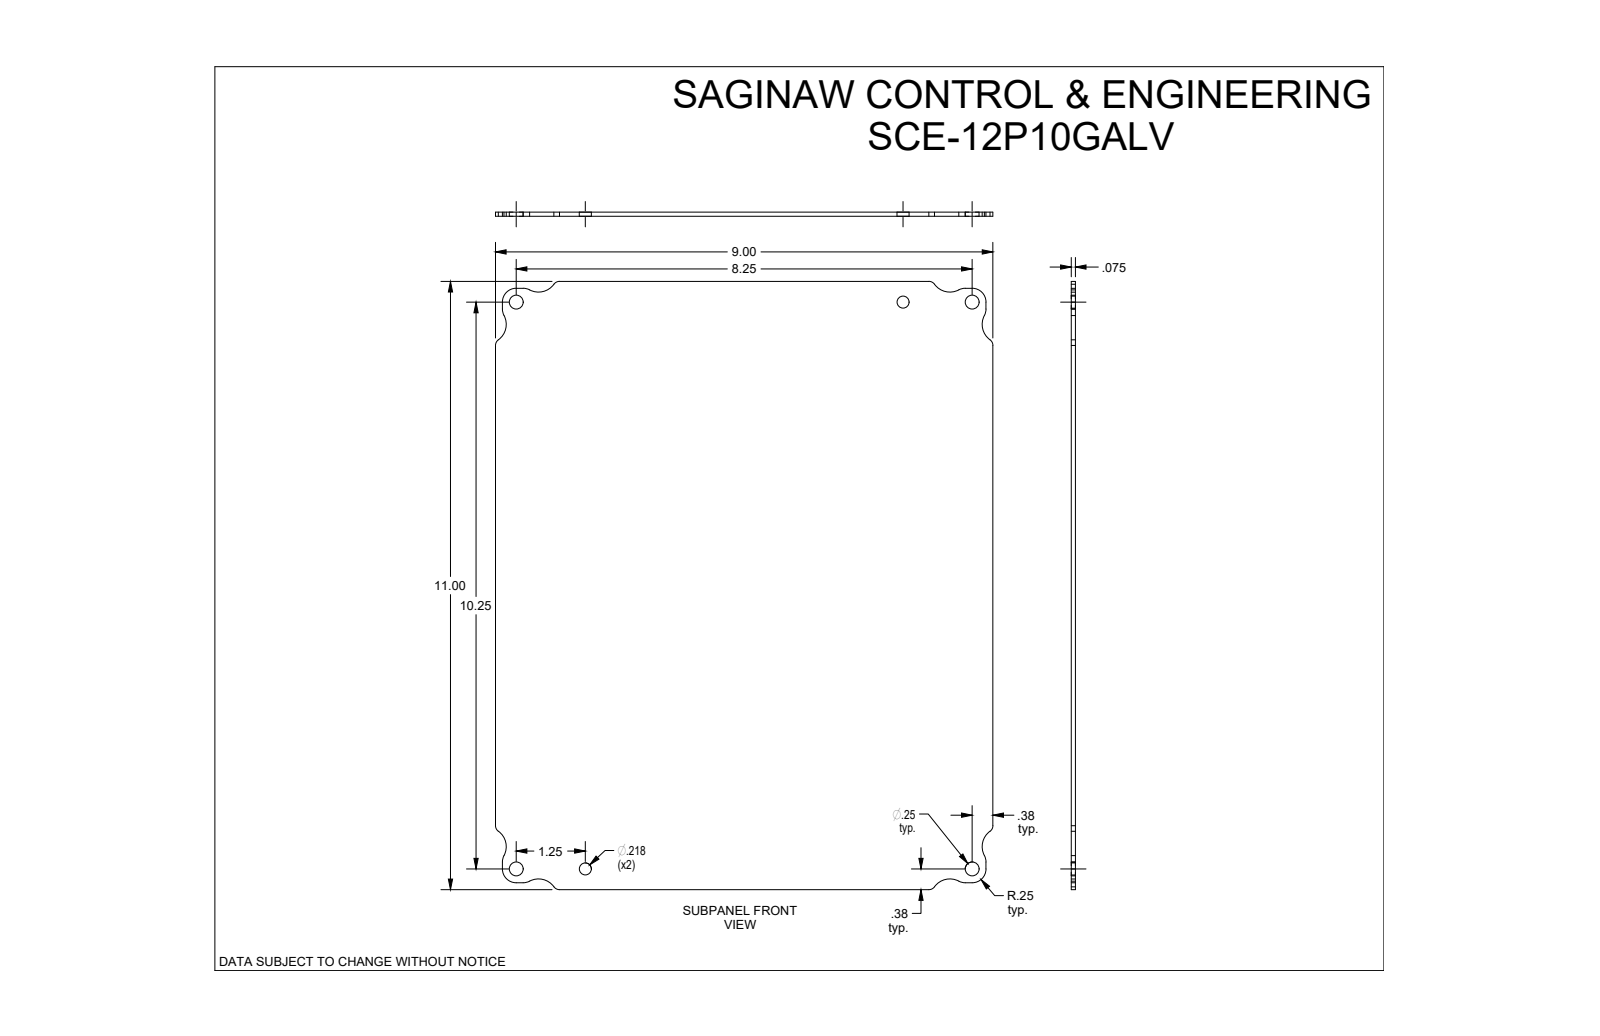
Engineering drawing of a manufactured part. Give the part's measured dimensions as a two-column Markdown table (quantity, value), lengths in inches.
| quantity | value |
| --- | --- |
| part name | SCE-12P10GALV |
| STEP written by | SolidWorks 2019 (CONFIG_CONTROL_DESIGN) |
| units | inches |
| bodies | 1 solid, 48 faces (14 planar, 34 cylindrical, 0 other) |
| overall size | 11 × 9 × 0.075 |
| volume | 7.315 in³ |
| surface area | 198.3 in² |
| round holes (diameter × count) | 0.25 × 4, 0.218 × 2 |
| partial cylindrical surfaces (radius × count) | 0.25 × 12, 0.125 × 8, 0.344 × 8 |
| main face-to-face distances | 0.075, 9, 11, 0.125, 10.875, 0.125, 8.875, 10.75, 8.75 |
| hole center spacings | 1.25, 7, 8.25, 10.25, 10.326, 12.412, 13.157, 11.752 |
